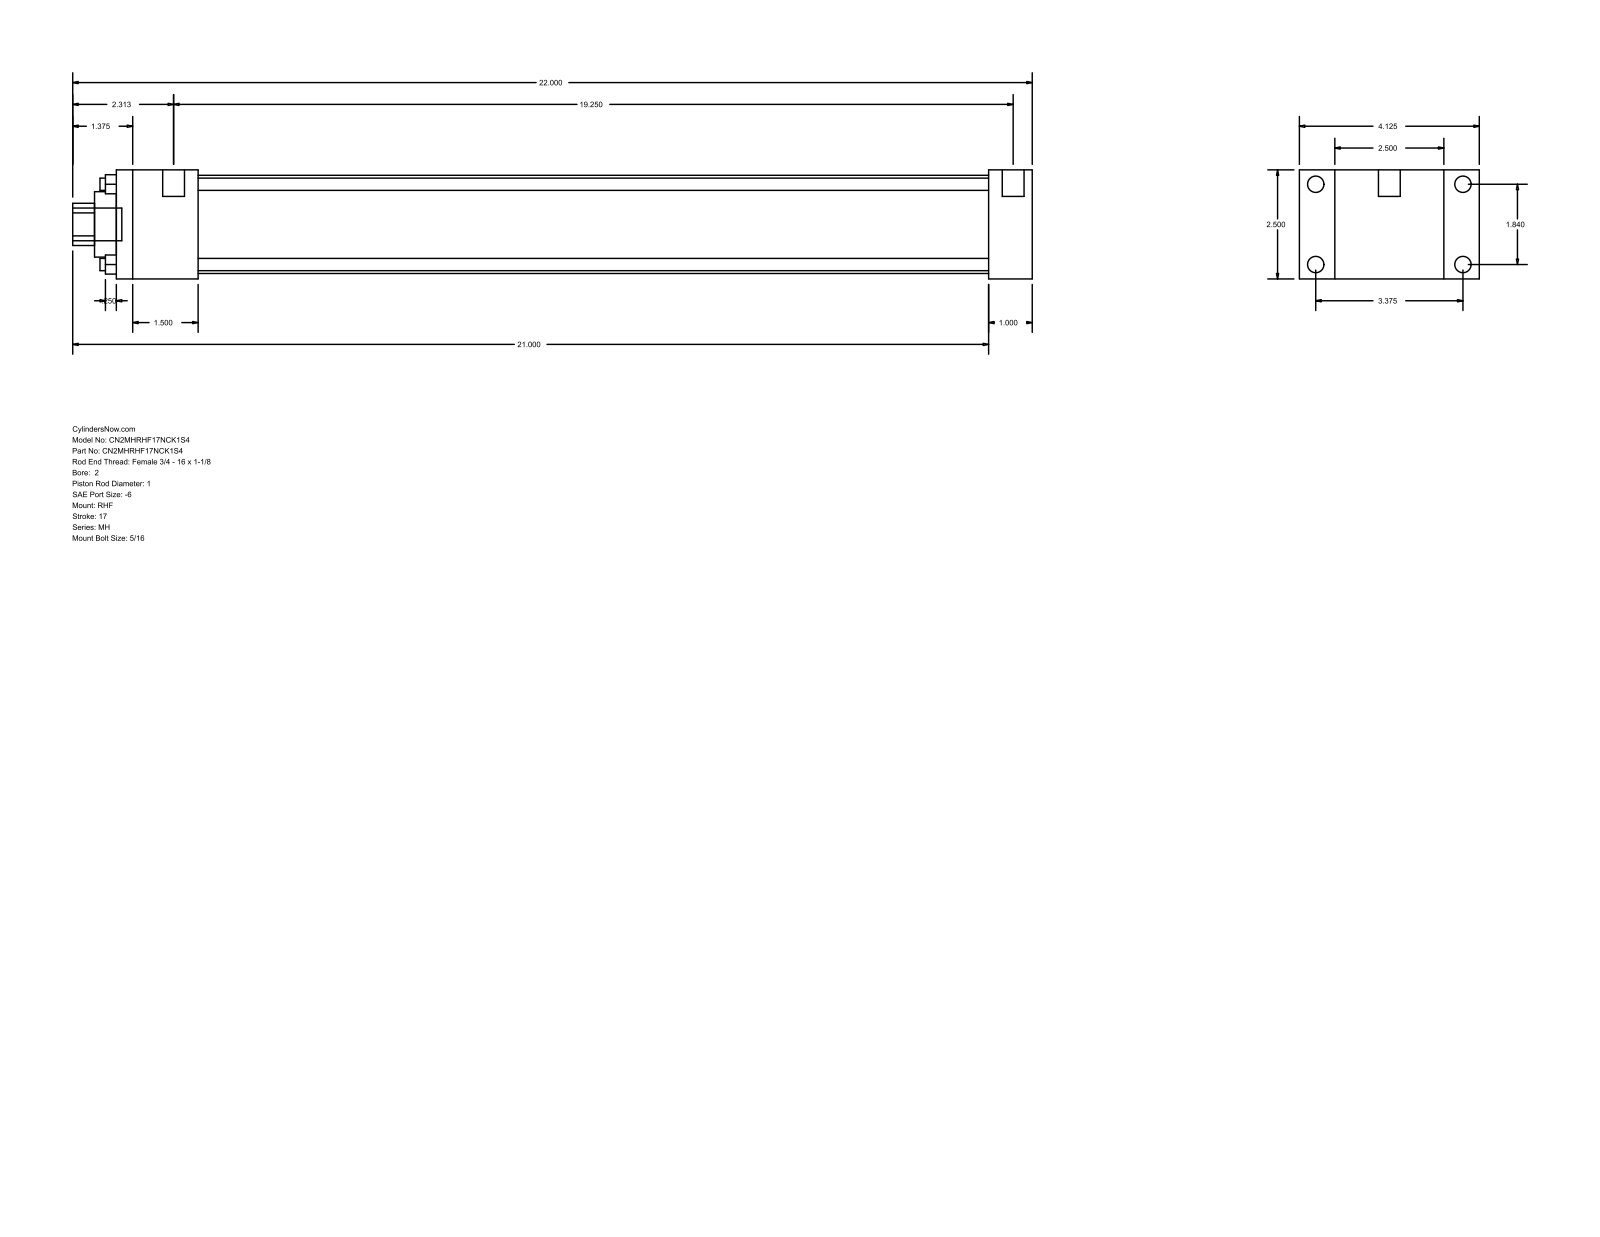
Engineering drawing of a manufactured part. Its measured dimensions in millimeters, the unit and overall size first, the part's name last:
Units: millimetres
Overall size (bounding box): 558.8 × 104.78 × 63.5
Round holes (diameter × count): ⌀7.14 ×4, ⌀25.4 ×1, ⌀38.1 ×1, ⌀57.15 ×1
Round bosses / shafts (diameter × count): ⌀9.53 ×4, ⌀5.56 ×4, ⌀12.7 ×2, ⌀19.05 ×1
Partial cylindrical surfaces — rounded edges, fillets, slot ends (radius × count): R12.29 ×1
Main face-to-face distances: 63.5, 25.4, 20.64, 84.14, 533.4, 508, 104.78, 47.63, 460.37, 485.77
Hole centre spacings: 33.05, 46.74, 66.1
Bodies: 0 solids, 88 faces (60 planar, 28 cylindrical, 0 other)
Part name (STEP PRODUCT): MH_RHF__0200_1
STEP written by: GSSL Pune (CONFIG_CONTROL_DESIGN)
